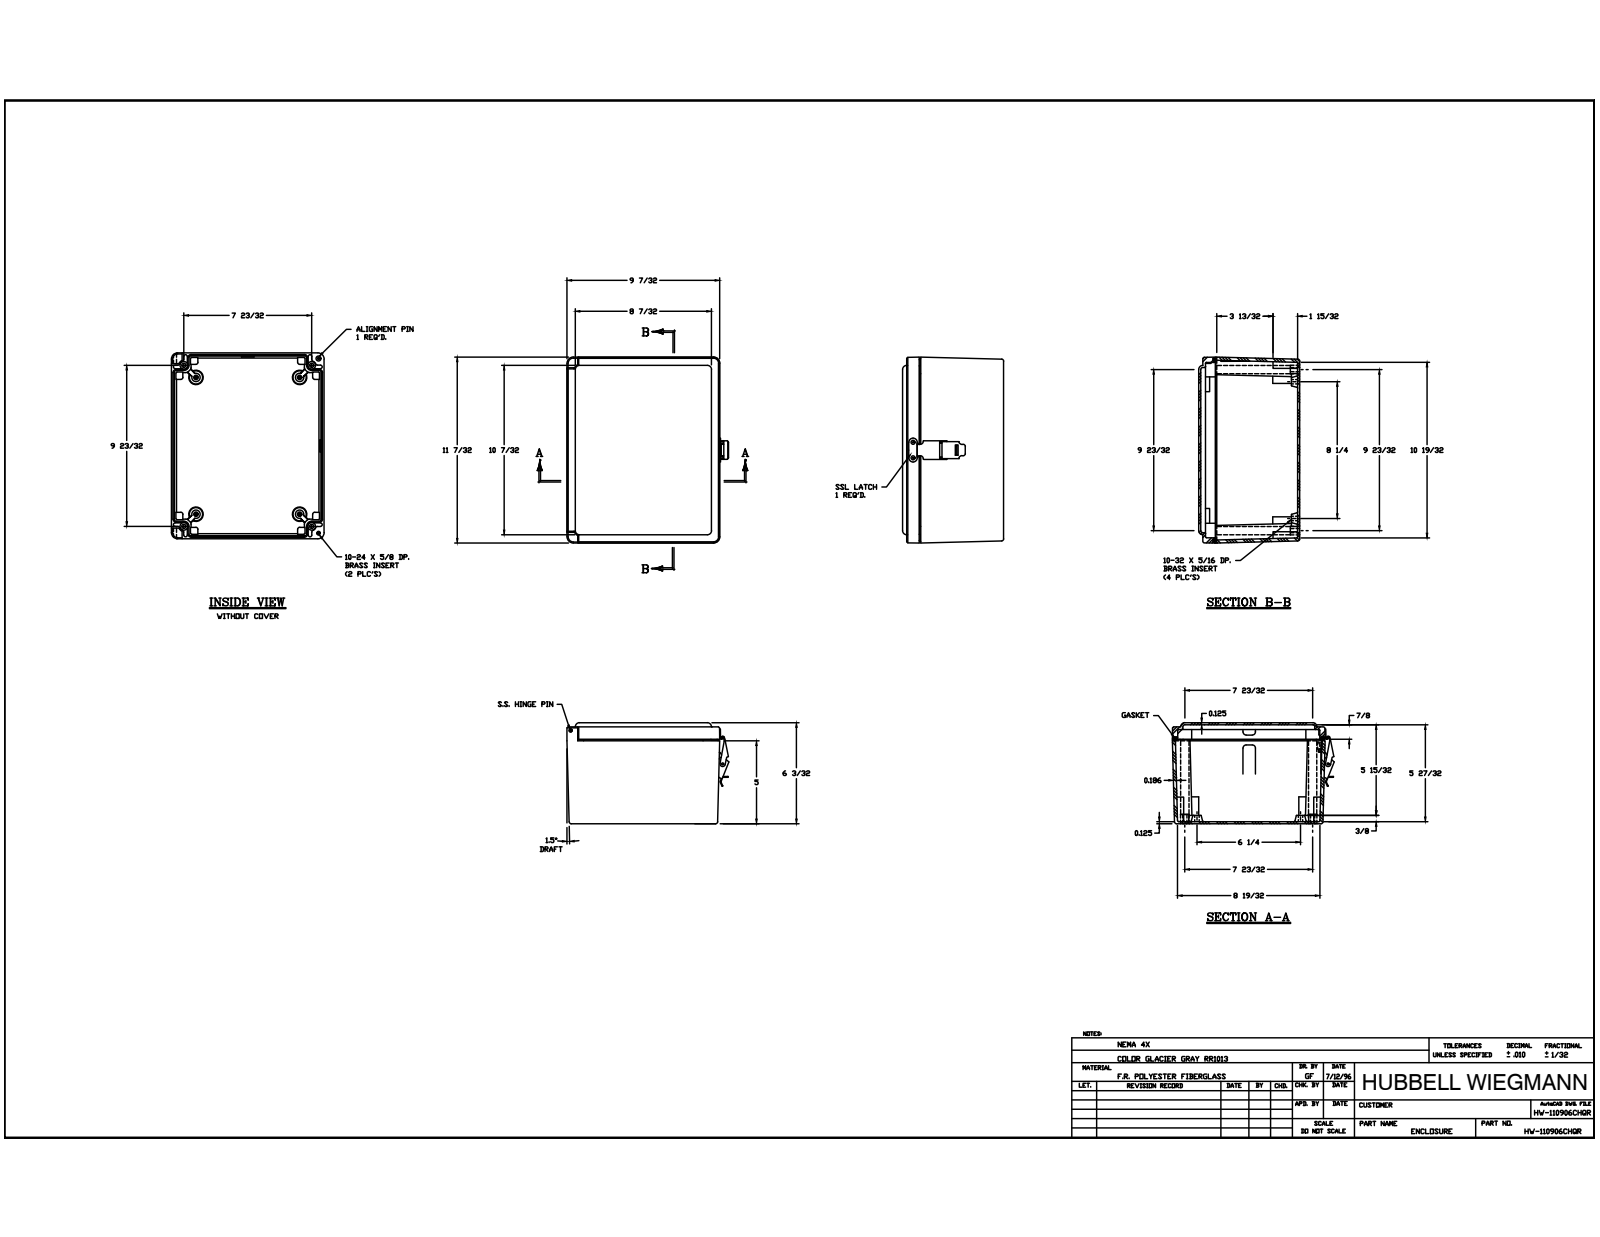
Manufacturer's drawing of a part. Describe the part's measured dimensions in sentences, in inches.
The part is named "WP1109HPLBOX; 0.3125-18 X 0.563 DP BRASS INSERT; 10-32 X0.3125 DP BRASS INSERT; 10-24 X 0.625 DP BRASS INSERT (+8 more)". Its 3-D file was written by "Autodesk Inventor 2014 (AUTOMOTIVE_DESIGN)". It is 30 solids with 1115 faces: 436 planar, 379 cylindrical and 300 other. Overall it measures 11.231 by 9.841 by 6.094 inches. Its volume is 83.72 cubic inches and its surface area 983.5 square inches. Round holes: 6 of diameter 0.281, 4 of diameter 0.104, 4 of diameter 0.14, 4 of diameter 0.156, 4 of diameter 0.156, 4 of diameter 0.313, 4 of diameter 0.531, 2 of diameter 0.096, 2 of diameter 0.13, 2 of diameter 0.135, 2 of diameter 0.145, 2 of diameter 0.179. Round bosses or shafts: 2 of diameter 0.375, 2 of diameter 0.371, 2 of diameter 0.234, 2 of diameter 0.095, 1 of diameter 0.3, 1 of diameter 0.299, 1 of diameter 0.185, 1 of diameter 0.178. Partial cylindrical surfaces (rounded edges, fillets, slot ends): 60 of radius 0.031, 38 of radius 0.125, 29 of radius 0.063, 10 of radius 0.25, 8 of radius 0.045, 8 of radius 0.059, 8 of radius 0.188, 8 of radius 0.375. The main face-to-face distances are 0.125, 5.969, 0.186, 6.094, 5.844, 0.125, 5.844, 5.719, 0.25, 0.75. The hole center spacings are 1.039, 7.035, 7.489, 8.147, 9.026, 11.396, 12.998, 9.471.
